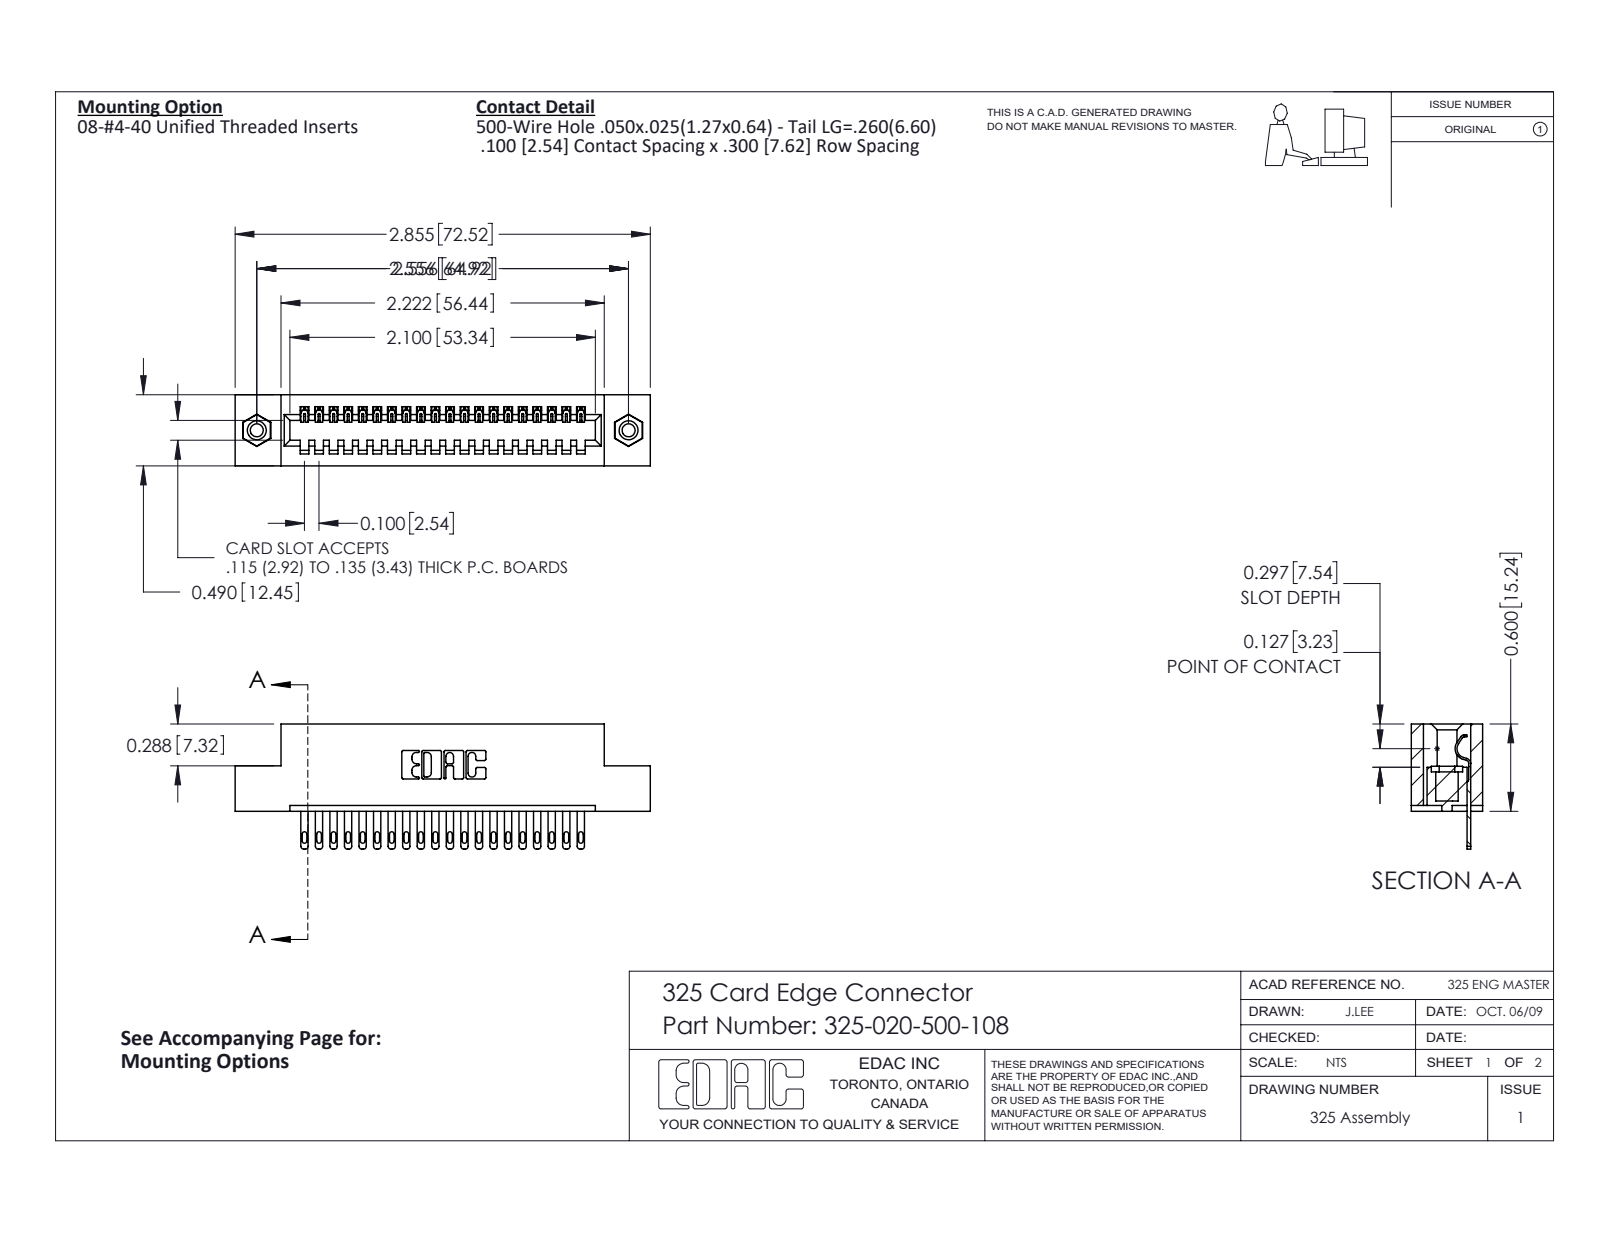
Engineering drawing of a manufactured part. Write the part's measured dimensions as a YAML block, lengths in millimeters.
part_name: "345-250-001_345-250-003-102; 325-292-001_325-293-100; 325 Part_TI; 325-020-500-108"
step_written_by: "SolidWorks 2016 (CONFIG_CONTROL_DESIGN)"
units: millimeters
bodies: {solids: 23, faces: 1254, planar: 822, cylindrical: 416, other: 16}
overall_size: [72.5, 21.8, 12.4]
volume: 9050
surface_area: 9561
round_holes:
  - {diameter: 2.3, count: 2}
  - {diameter: 3.2, count: 2}
  - {diameter: 4.1, count: 2}
round_bosses_or_shafts:
  - {diameter: 3.9, count: 2}
partial_cylinders:
  - {radius: 0.2, count: 40}
  - {radius: 0.4, count: 40}
  - {radius: 0.5, count: 40}
  - {radius: 0.3, count: 22}
  - {radius: 0.2, count: 6}
  - {radius: 0.8, count: 6}
  - {radius: 0.7, count: 3}
  - {radius: 0.4, count: 1}
face_to_face_distances: [2.1, 10.3, 7.6, 12.4, 2.7, 9.7, 0.6, 1, 2.5, 8.3]
hole_center_spacings: [64.9]
